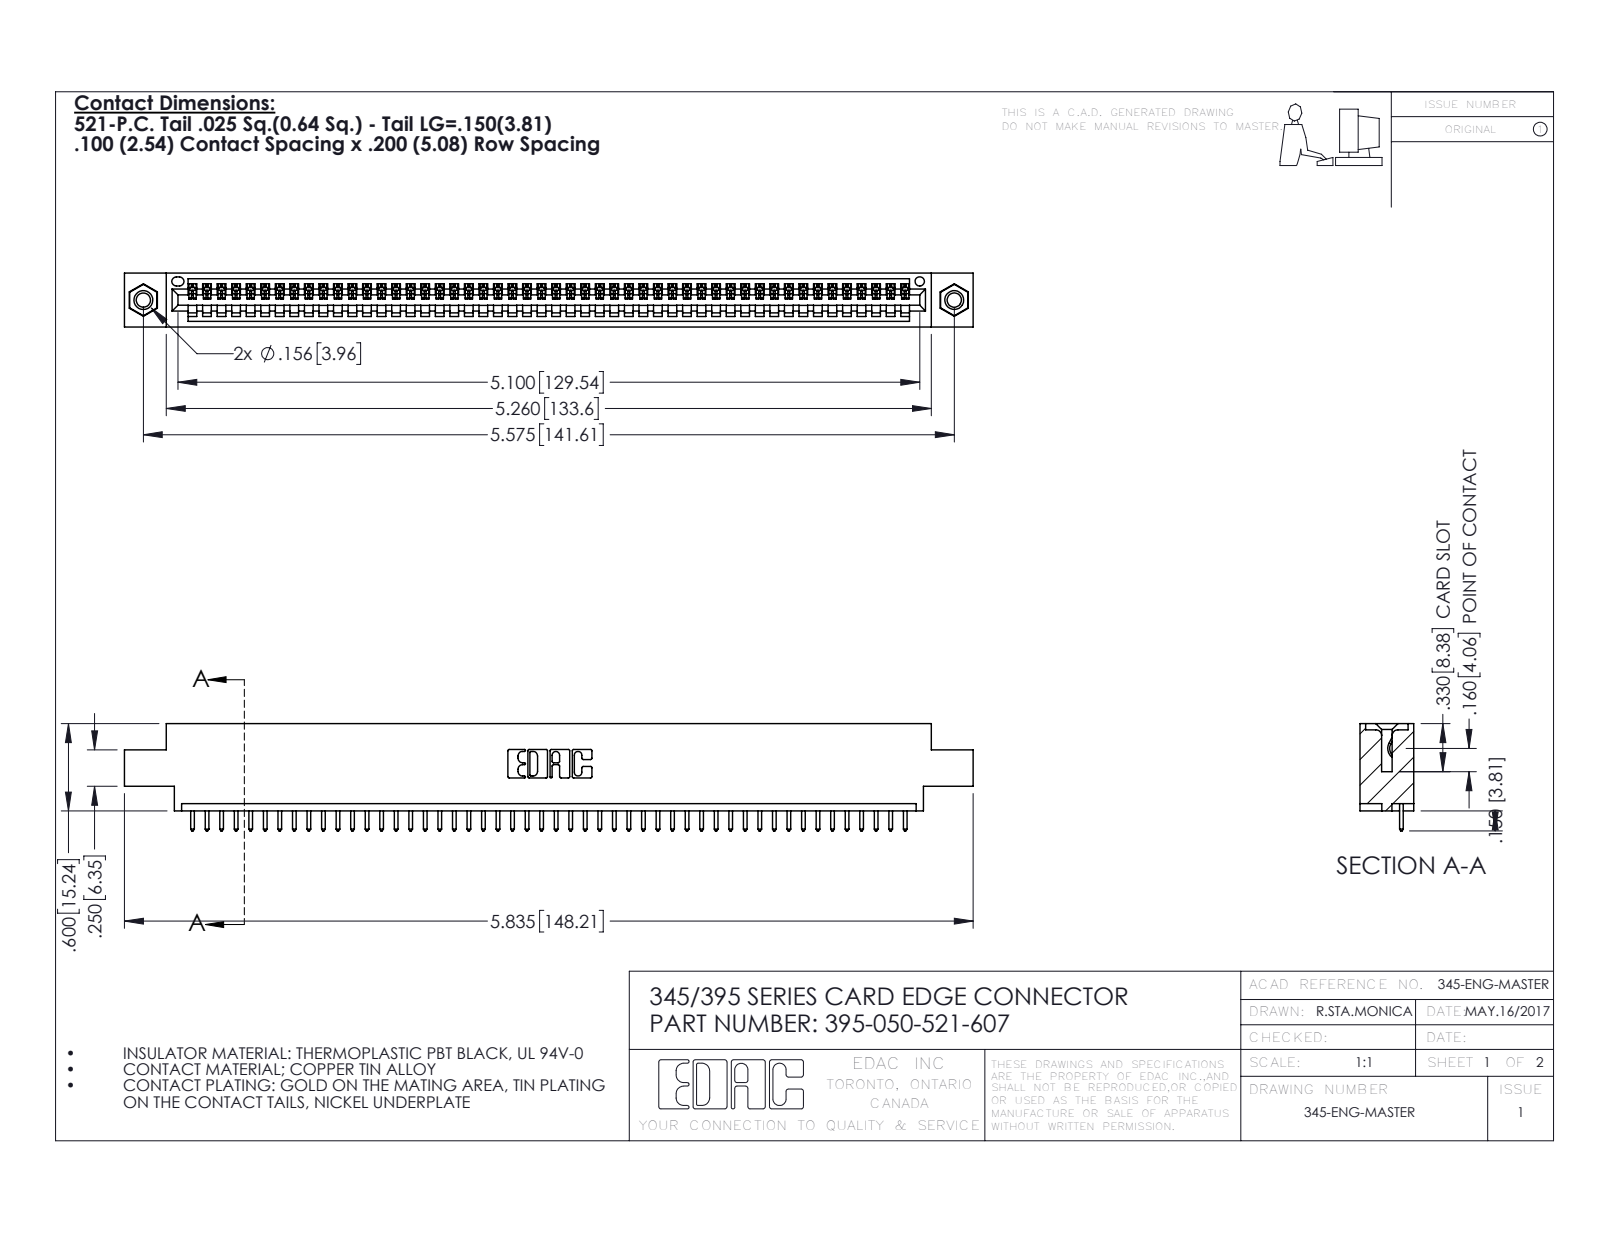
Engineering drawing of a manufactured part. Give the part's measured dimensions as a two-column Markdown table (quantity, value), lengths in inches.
| quantity | value |
| --- | --- |
| part name | 345-250-001_345-250-005-103; 345 Part_0.170 Offset - 0.156 Dia-TI; 395-050-521-607; 345-292-001_345-293-121 |
| STEP written by | SolidWorks 2016 (CONFIG_CONTROL_DESIGN) |
| units | inches |
| bodies | 53 solids, 3090 faces (2116 planar, 958 cylindrical, 16 other) |
| overall size | 5.835 × 0.737 × 0.37 |
| volume | 0.847 in³ |
| surface area | 28.13 in² |
| round holes (diameter × count) | 0.098 × 2, 0.125 × 2, 0.156 × 2, 0.064 × 1 |
| round bosses / shafts (diameter × count) | 0.155 × 2 |
| partial cylindrical surfaces (radius × count) | 0.006 × 100, 0.01 × 100, 0.01 × 22, 0.007 × 6, 0.031 × 6, 0.026 × 3, 0.031 × 2, 0.04 × 2 |
| main face-to-face distances | 0.072, 0.298, 0.37, 0.2, 0.098, 0.272, 0.025, 0.225, 0.175, 0.149 |
| hole center spacings | 0.27, 5.339, 5.575 |
